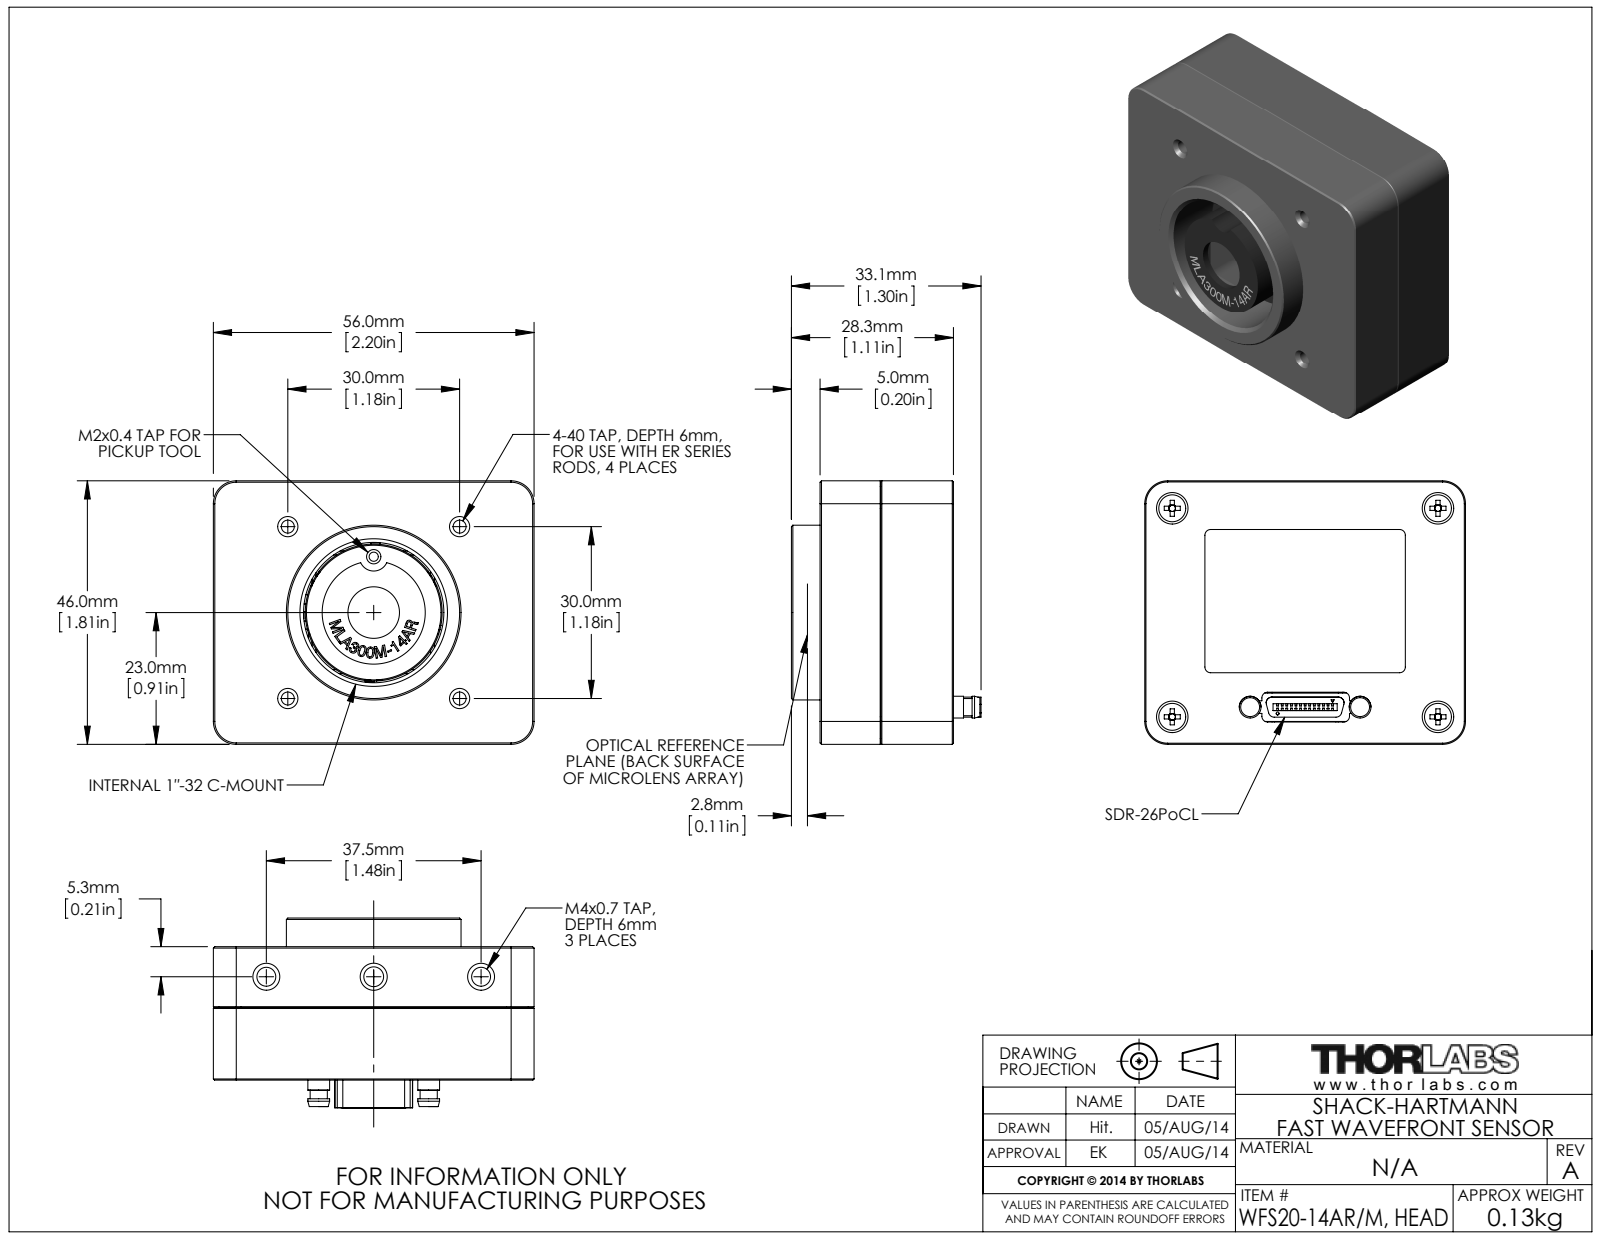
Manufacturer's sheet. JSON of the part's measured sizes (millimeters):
{"part_name": "Kugel 2mm; Halter Teil3 Typ300-14AR; Stift 1x4; Halter Teil2 Baugruppe (+8 more)", "step_written_by": "SolidWorks 2014 (AUTOMOTIVE_DESIGN)", "units": "millimeters", "bodies": {"solids": 41, "faces": 2417, "planar": 1169, "cylindrical": 660, "other": 588}, "overall_size": [56, 46, 33.11], "volume_mm3": 72219, "surface_area_mm2": 44089, "round_holes": [[0.6, 26], [3.2, 6], [2.05, 4], [2.26, 4], [2.7, 4], [2.9, 4], [3, 4], [6, 4], [1.9, 3], [1.2, 2], [1.75, 2], [3.3, 2]], "round_bosses_or_shafts": [[0.7, 108], [1, 11], [3, 8], [5.6, 4], [4.7, 4], [2.5, 4], [2.1, 4], [3.8, 2]], "partial_cylinders_radius": [[1, 19], [2, 12], [0.18, 6], [0.2, 4], [1.5, 4], [2.75, 4], [3.1, 4], [3.5, 4]], "face_to_face_distances": [14.98, 1.61, 16.59, 3.5, 19.39, 3.9, 13.5, 1.48, 3.09, 5.89], "hole_center_spacings": [1.4, 1.6, 2.66, 5.72, 3.2, 3.5, 4.16, 4.46]}
